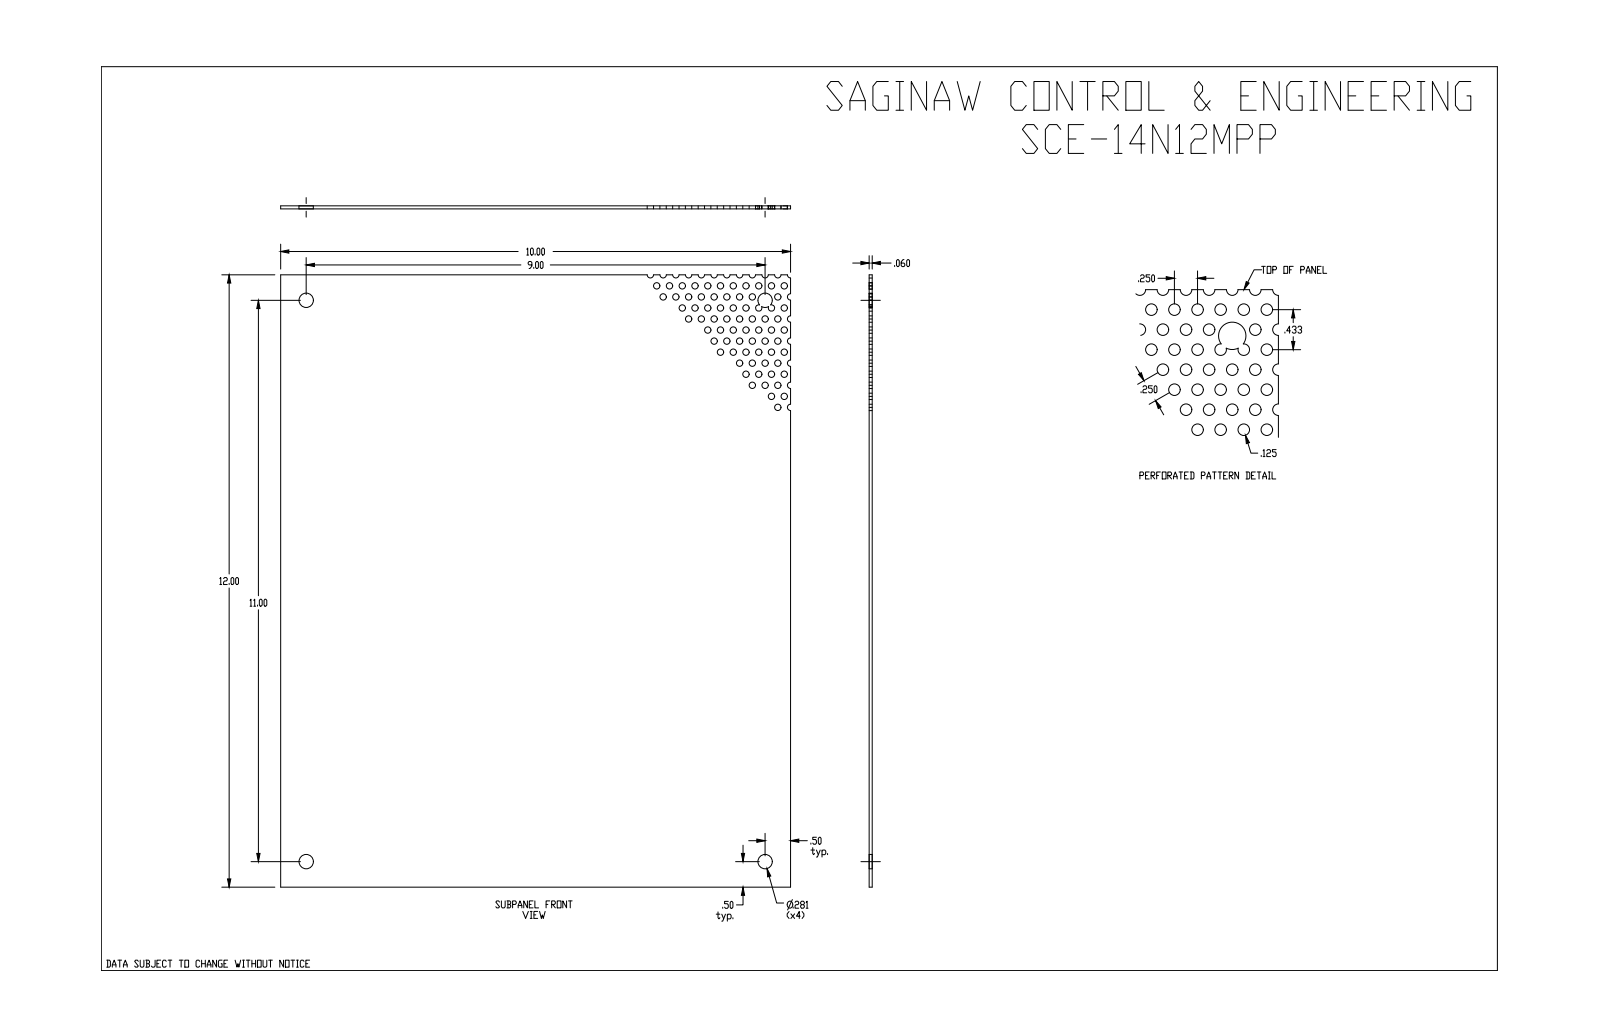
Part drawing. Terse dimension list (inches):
name: SCE-14N12MPP
written by: SolidWorks 2019 (CONFIG_CONTROL_DESIGN)
unit: in
bodies: 1 solid, 116 faces (23 planar, 93 cylindrical, 0 other)
size: 12 × 10 × 0.06
volume: 7.127 in³; area: 242.1 in²
holes: 63× ⌀0.125, 7× ⌀0.125, 4× ⌀0.281
rounds: 10× R0.063, 8× R0.062
face distances: 0.06, 10, 12
hole spacings: 0.25, 0.661, 0.5, 0.433, 1.323, 0.433, 1.09, 0.75
